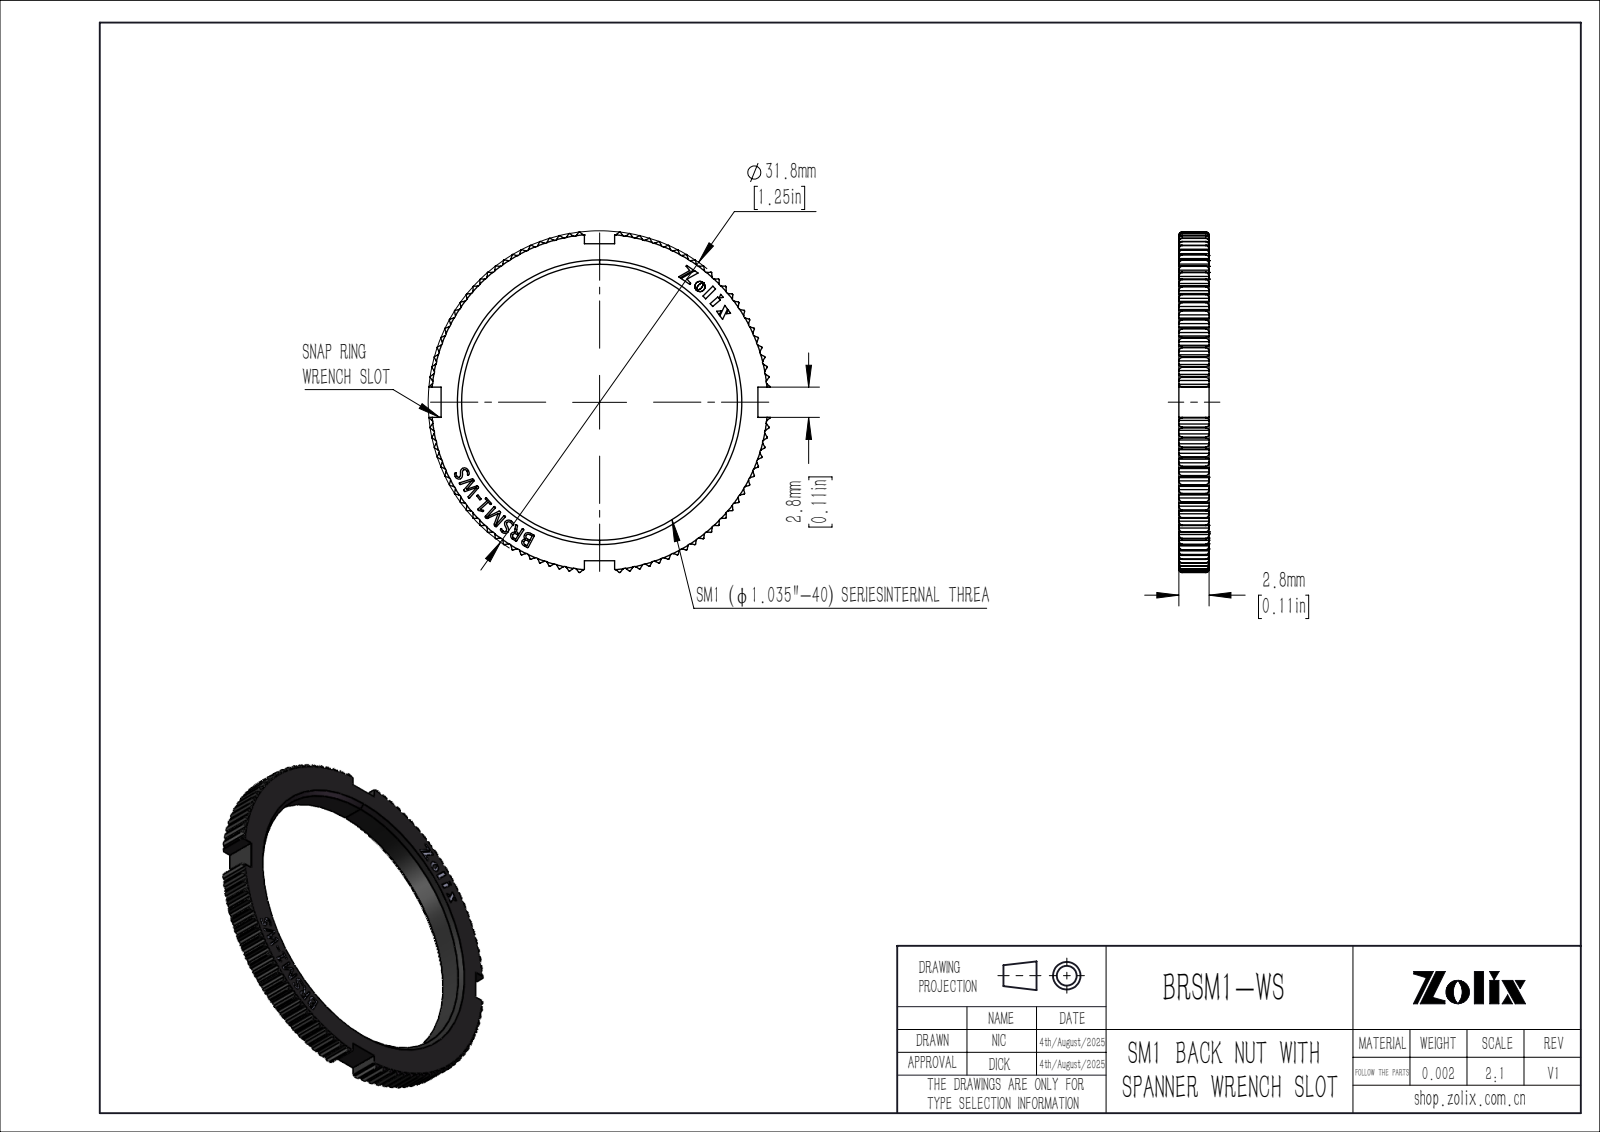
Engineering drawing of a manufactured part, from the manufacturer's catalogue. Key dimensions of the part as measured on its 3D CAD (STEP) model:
Part name (STEP PRODUCT): BRSM1-WS
STEP written by: SolidWorks 2020 (CONFIG_CONTROL_DESIGN)
Units: millimetres
Bodies: 1 solid, 931 faces (437 planar, 218 cylindrical, 276 other)
Overall size (bounding box): 31.68 × 31.59 × 2.8
Volume: 686 mm³ · Surface area: 1 046 mm²
Round holes (diameter × count): ⌀25.6 ×1
Partial cylindrical surfaces — rounded edges, fillets, slot ends (radius × count): R0.25 ×96, R15.9 ×1
Main face-to-face distances: 2.8, 21.88, 21.86, 13.3, 16.1, 29.4, 2.78, 21.9, 1.25, 1.3
